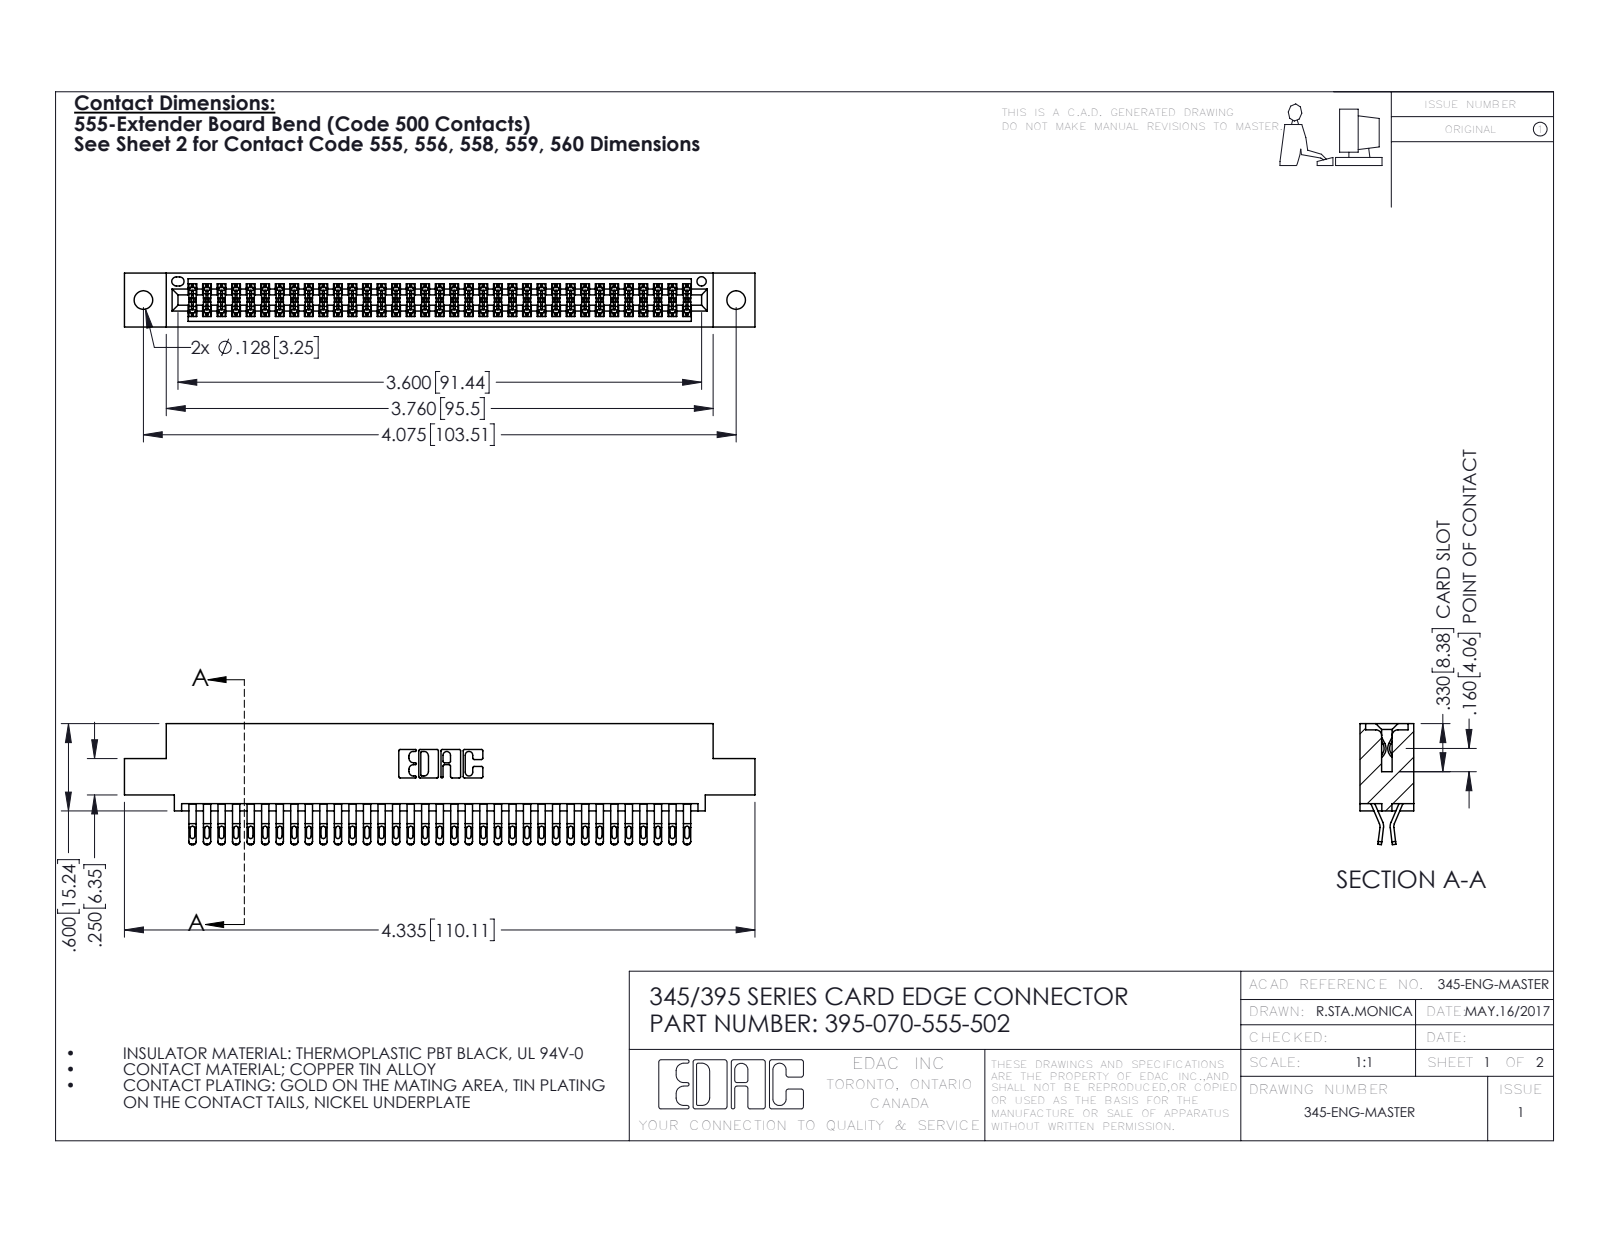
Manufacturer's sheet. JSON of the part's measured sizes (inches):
{"part_name": "345-292-001_555 Tail; 395-070-555-502; 345 Part_0.110 Offset - 0.128 Dia", "step_written_by": "SolidWorks 2016 (CONFIG_CONTROL_DESIGN)", "units": "inches", "bodies": {"solids": 71, "faces": 4050, "planar": 2254, "cylindrical": 1796, "other": 0}, "overall_size": [4.335, 0.832, 0.37], "volume_in3": 0.654, "surface_area_in2": 25.18, "round_holes": [[0.128, 2], [0.064, 1]], "partial_cylinders_radius": [[0.016, 175], [0.02, 140], [0.006, 105], [0.01, 22], [0.007, 6], [0.031, 6], [0.026, 3], [0.01, 2]], "face_to_face_distances": [0.298, 0.072, 0.37, 0.025, 0.2, 0.098, 0.272, 0.225, 0.175, 0.149], "hole_center_spacings": [0.27, 3.839, 4.075]}
